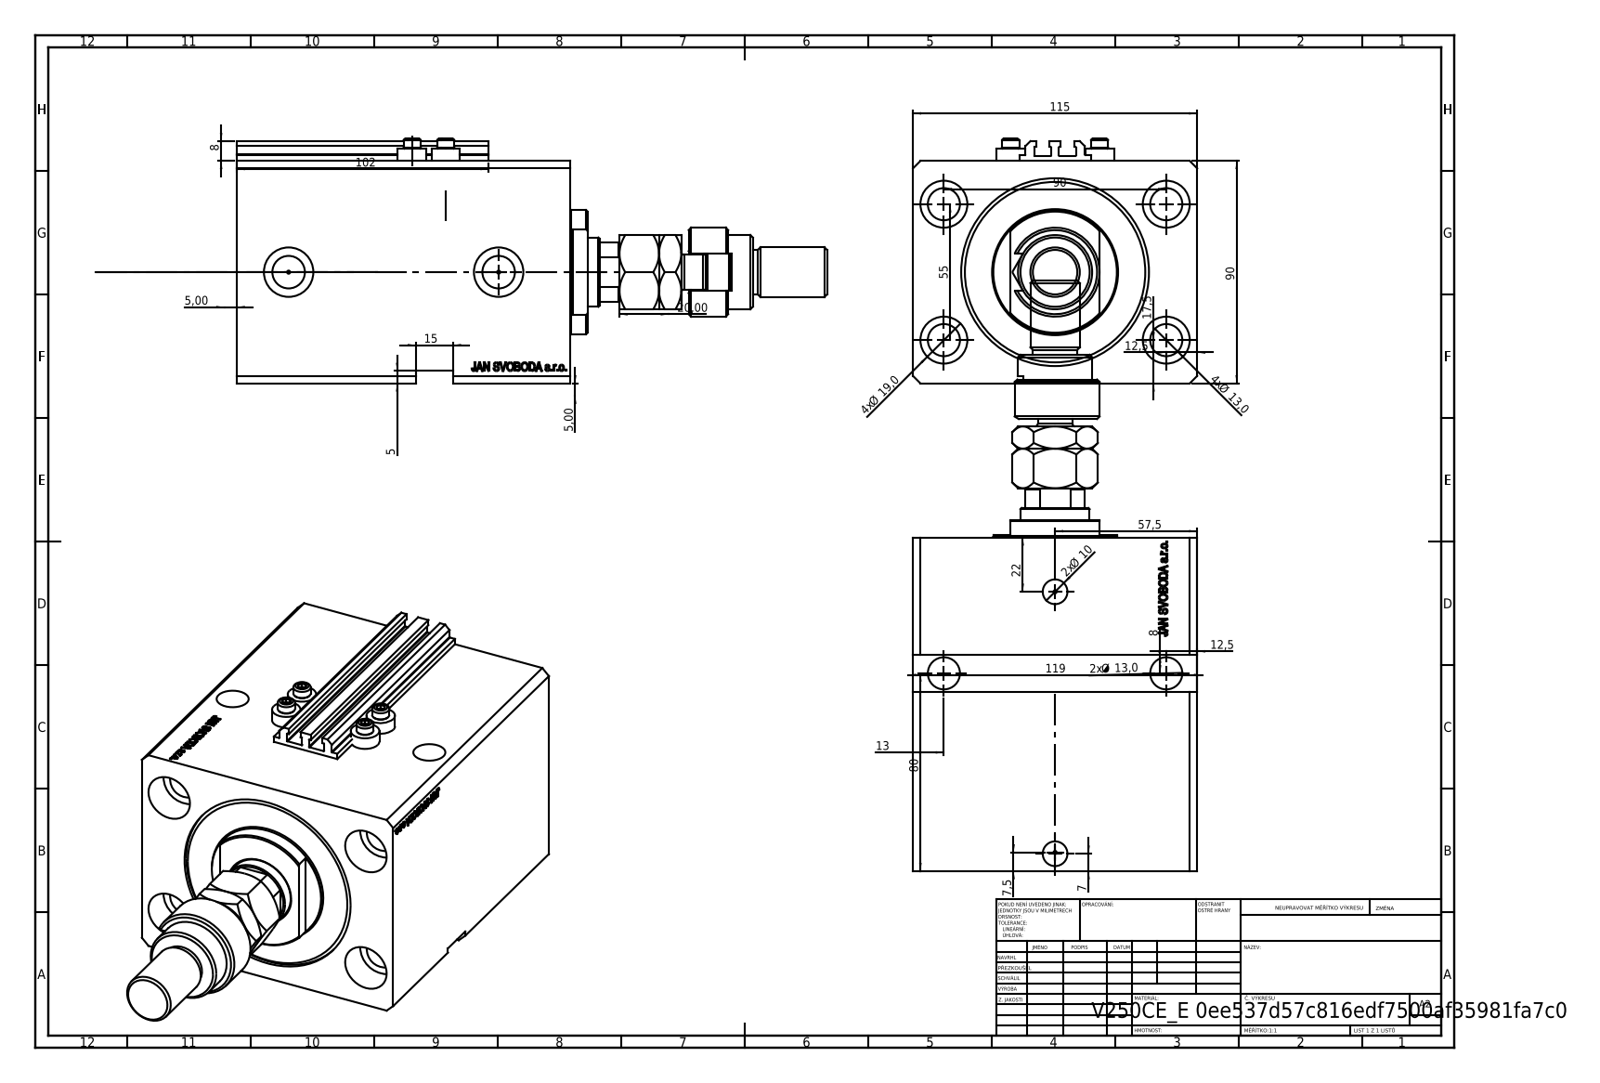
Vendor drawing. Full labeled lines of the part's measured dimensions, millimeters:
Part name (STEP PRODUCT): V250CE_VC_E; V250CE_E; ALLEN BOLT V250CE; MFA (+2 more)
STEP written by: SolidWorks 2019 (CONFIG_CONTROL_DESIGN)
Units: millimetres
Bodies: 10 solids, 1192 faces (571 planar, 139 cylindrical, 482 other)
Overall size (bounding box): 238.9 × 115 × 99
Volume: 1 226 000 mm³ · Surface area: 198 324 mm²
Round holes (diameter × count): ⌀13 ×6, ⌀1.25 ×4, ⌀4 ×4, ⌀19 ×4, ⌀10 ×2, ⌀13.16 ×2, ⌀20 ×2, ⌀18.5 ×1, ⌀28 ×1, ⌀63 ×1, ⌀76 ×1
Round bosses / shafts (diameter × count): ⌀11.6 ×4, ⌀7 ×4, ⌀50 ×1, ⌀36 ×1, ⌀30 ×1, ⌀22 ×1, ⌀20 ×1, ⌀18 ×1
Partial cylindrical surfaces — rounded edges, fillets, slot ends (radius × count): R0.2 ×10, R7.5 ×1, R12 ×1, R13.5 ×1
Main face-to-face distances: 90, 115, 135, 87, 17.9, 117.1, 104.9, 30.1, 50, 54.9
Hole centre spacings: 52.74, 90, 13.6, 27.39, 28.46, 33.62, 36, 38.48
